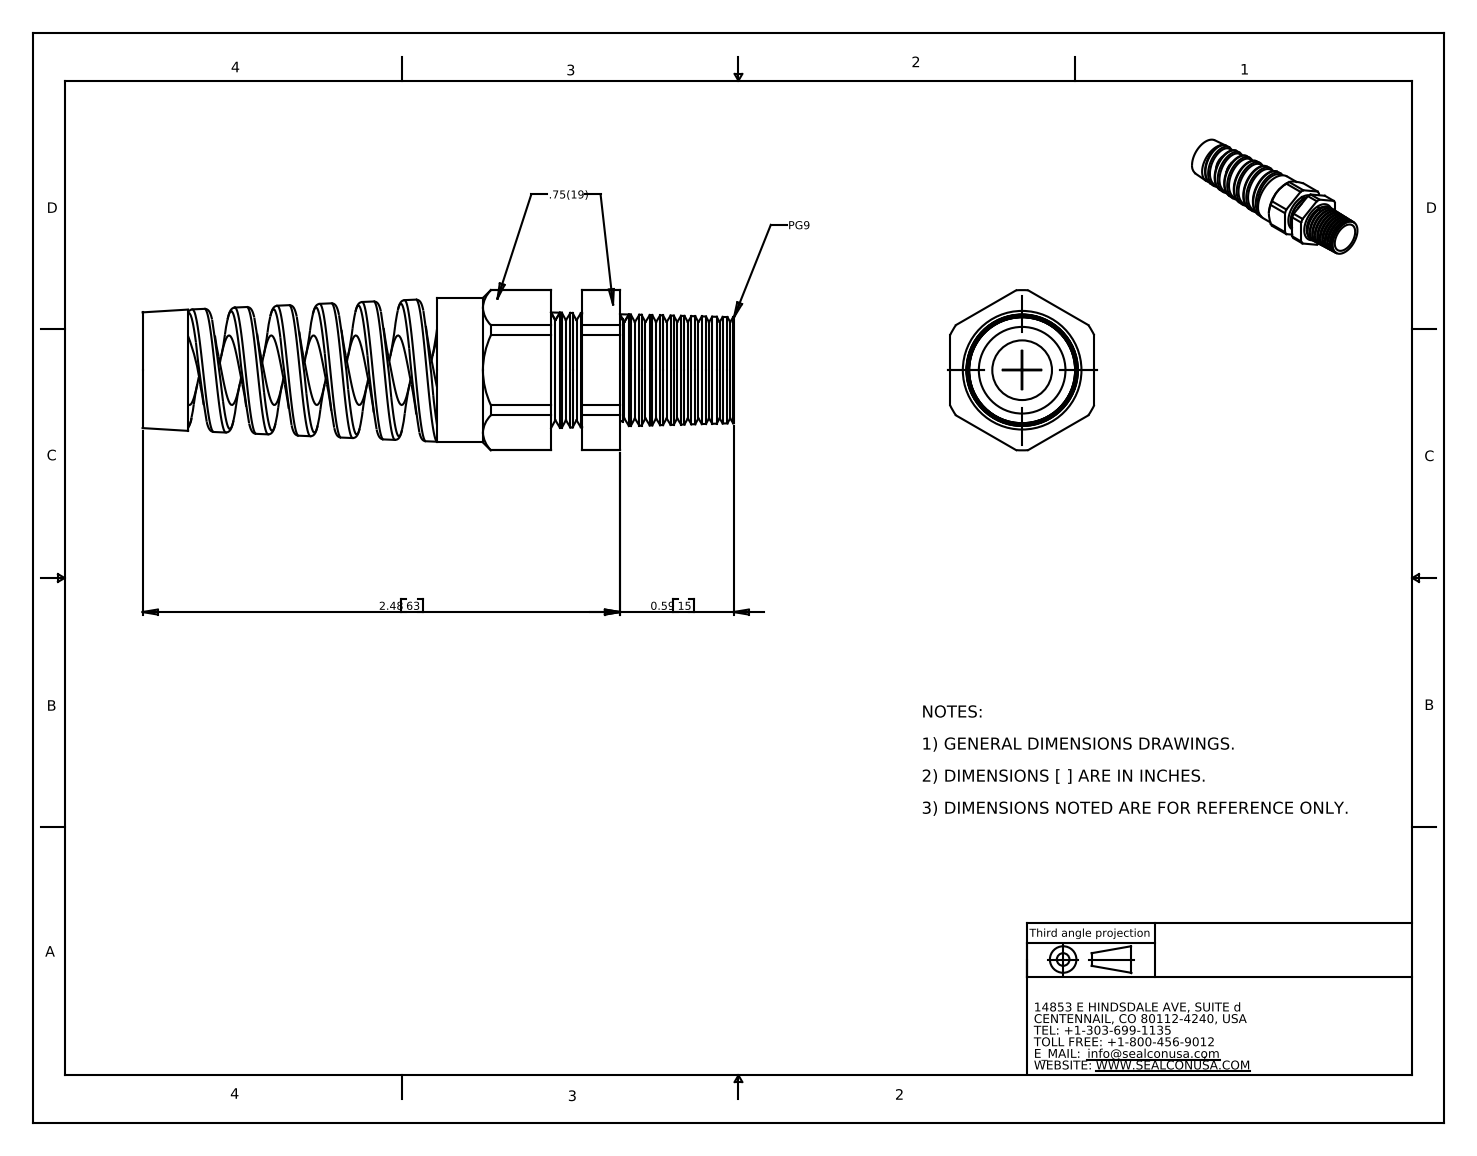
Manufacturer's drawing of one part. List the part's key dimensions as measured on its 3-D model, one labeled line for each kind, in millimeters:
Part name (STEP PRODUCT): CF09CCA-BK
STEP written by: SolidWorks 2007 (CONFIG_CONTROL_DESIGN)
Units: millimetres
Bodies: 2 solids, 182 faces (24 planar, 38 cylindrical, 120 other)
Overall size (bounding box): 78 × 21.2 × 19.1
Volume: 10 000 mm³ · Surface area: 8 748 mm²
Round holes (diameter × count): ⌀7.9 ×1, ⌀9.2 ×1, ⌀9.9 ×1
Round bosses / shafts (diameter × count): ⌀19.1 ×1, ⌀11.4 ×1
Partial cylindrical surfaces — rounded edges, fillets, slot ends (radius × count): R10.6 ×1
Main face-to-face distances: 19.1, 4.1, 19.1, 9.1, 5, 15.1, 19.2, 24.2, 38.8, 53.9
